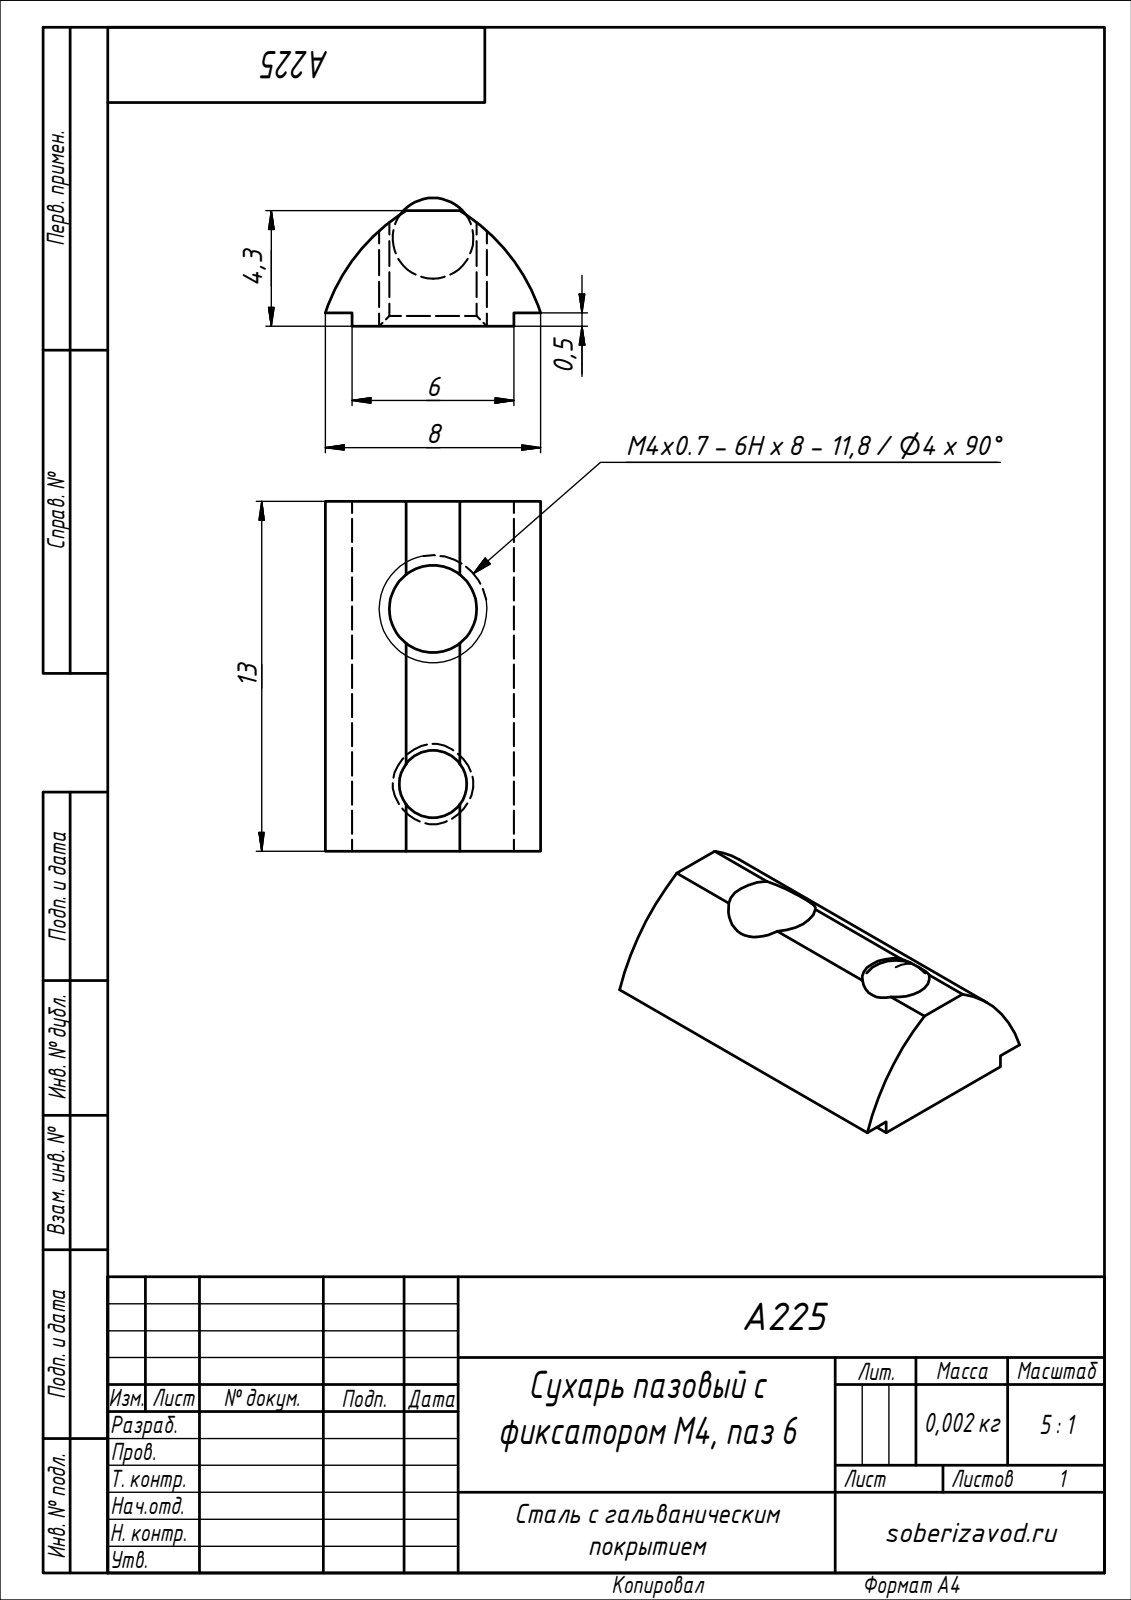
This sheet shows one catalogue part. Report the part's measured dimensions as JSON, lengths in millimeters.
{"part_name": "A225", "step_written_by": "Autodesk Inventor 2018 (AP242_MANAGED_MODEL_BASED_3D_ENGINEERING_MIM_LF)", "units": "millimeters", "bodies": {"solids": 2, "faces": 17, "planar": 11, "cylindrical": 4, "other": 2}, "overall_size": [13, 8, 4.77], "volume_mm3": 290, "surface_area_mm2": 387, "round_holes": [[2.5, 1], [3.24, 1]], "partial_cylinders_radius": [[7.12, 2]], "face_to_face_distances": [0.5, 13, 4.3, 3.8, 6, 2.3, 1.8, 2], "hole_center_spacings": [6.5]}
